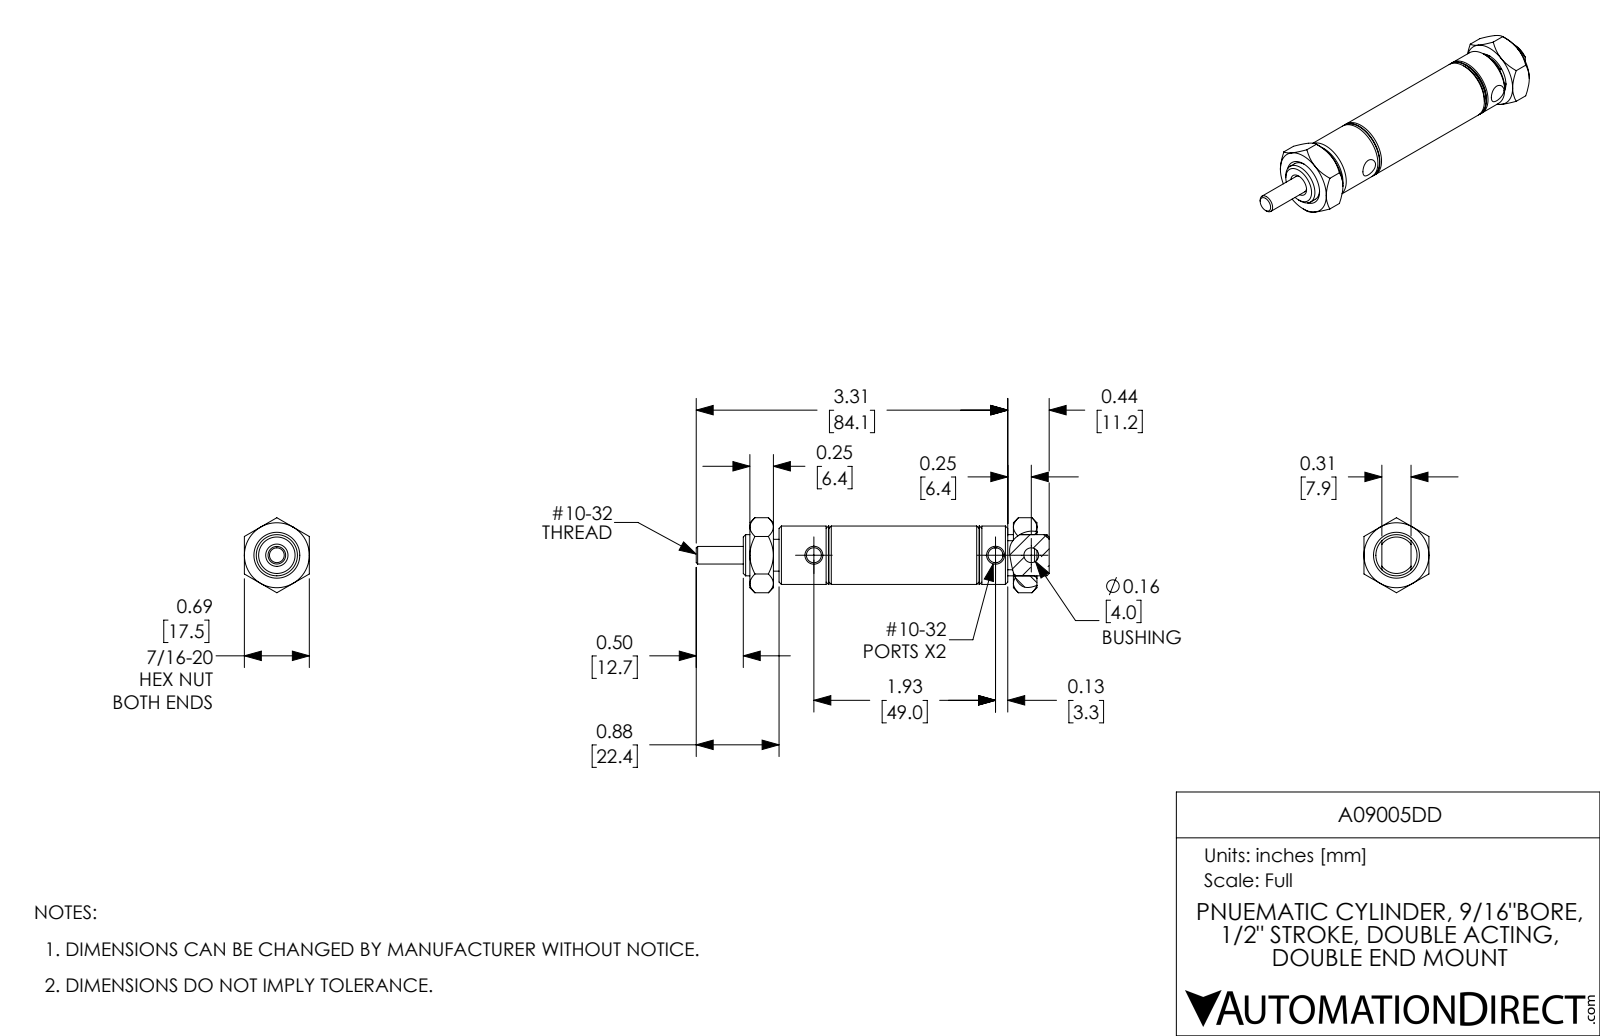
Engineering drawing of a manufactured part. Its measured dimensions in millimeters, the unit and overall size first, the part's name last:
Units: millimetres
Overall size (bounding box): 95.3 × 20.2 × 17.5
Round holes (diameter × count): ⌀4 ×2, ⌀4.8 ×2, ⌀4 ×1, ⌀4 ×1, ⌀4.7 ×1, ⌀14.3 ×1
Round bosses / shafts (diameter × count): ⌀15.7 ×1, ⌀11.1 ×1, ⌀8.6 ×1
Main face-to-face distances: 12.7, 17.5, 18.2, 6.4, 71.1, 30.9, 43.6, 45.1, 7.9, 25.4
Hole centre spacings: 9.7, 49, 58.7
Volume: 13 700 mm³ · Surface area: 9 994 mm²
Bodies: 4 solids, 151 faces (36 planar, 46 cylindrical, 69 other)
Part name (STEP PRODUCT): A09005DD; A09005DD-Rod; A09005DD_Mounting Nut_D-154; A09005DD-MainBody
STEP written by: SolidWorks 2017 (AUTOMOTIVE_DESIGN)
